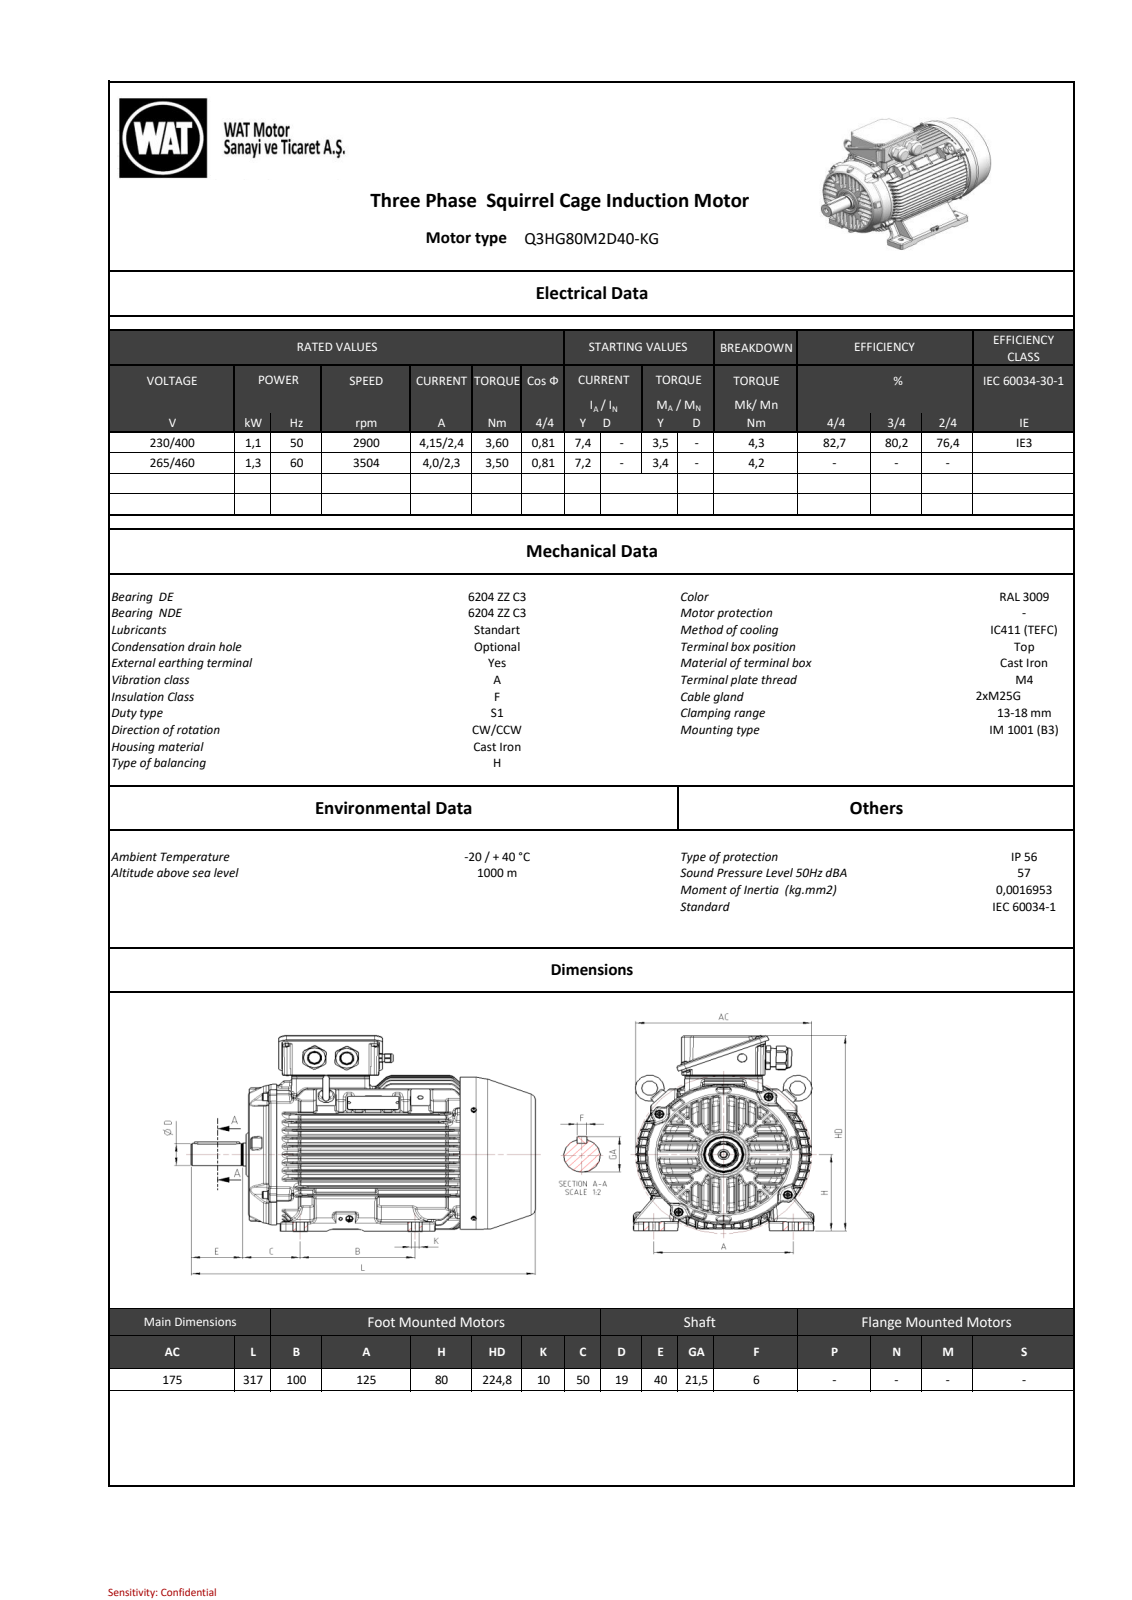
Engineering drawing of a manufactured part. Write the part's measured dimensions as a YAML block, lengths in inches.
part_name: "C901B65877A5yhnl"
step_written_by: "SIEMENS PLM Software NX 11.0 (AUTOMOTIVE_DESIGN)"
units: inches
bodies: {solids: 0, faces: 3005, planar: 806, cylindrical: 854, other: 1345}
overall_size: [12.471, 8.857, 8.714]
round_holes:
  - {diameter: 0.394, count: 3}
  - {diameter: 0.098, count: 2}
  - {diameter: 0.165, count: 2}
  - {diameter: 0.677, count: 2}
  - {diameter: 0.197, count: 1}
  - {diameter: 0.252, count: 1}
  - {diameter: 0.256, count: 1}
  - {diameter: 1.094, count: 1}
  - {diameter: 1.102, count: 1}
  - {diameter: 6.614, count: 1}
round_bosses_or_shafts:
  - {diameter: 0.787, count: 4}
  - {diameter: 0.341, count: 3}
  - {diameter: 0.335, count: 3}
  - {diameter: 0.315, count: 3}
  - {diameter: 0.197, count: 3}
  - {diameter: 1.091, count: 2}
  - {diameter: 0.994, count: 2}
  - {diameter: 6.693, count: 1}
partial_cylinders:
  - {radius: 0.059, count: 311}
  - {radius: 0.079, count: 56}
  - {radius: 0.098, count: 46}
  - {radius: 0.039, count: 34}
  - {radius: 0.157, count: 24}
  - {radius: 0.197, count: 22}
  - {radius: 0.008, count: 18}
  - {radius: 0.118, count: 13}
face_to_face_distances: [1.645, 2.463, 0.119, 0.059, 10.615, 8.97, 6.022, 8.485, 0.197, 0.118]
hole_center_spacings: [1.575, 2.952, 4.541]
